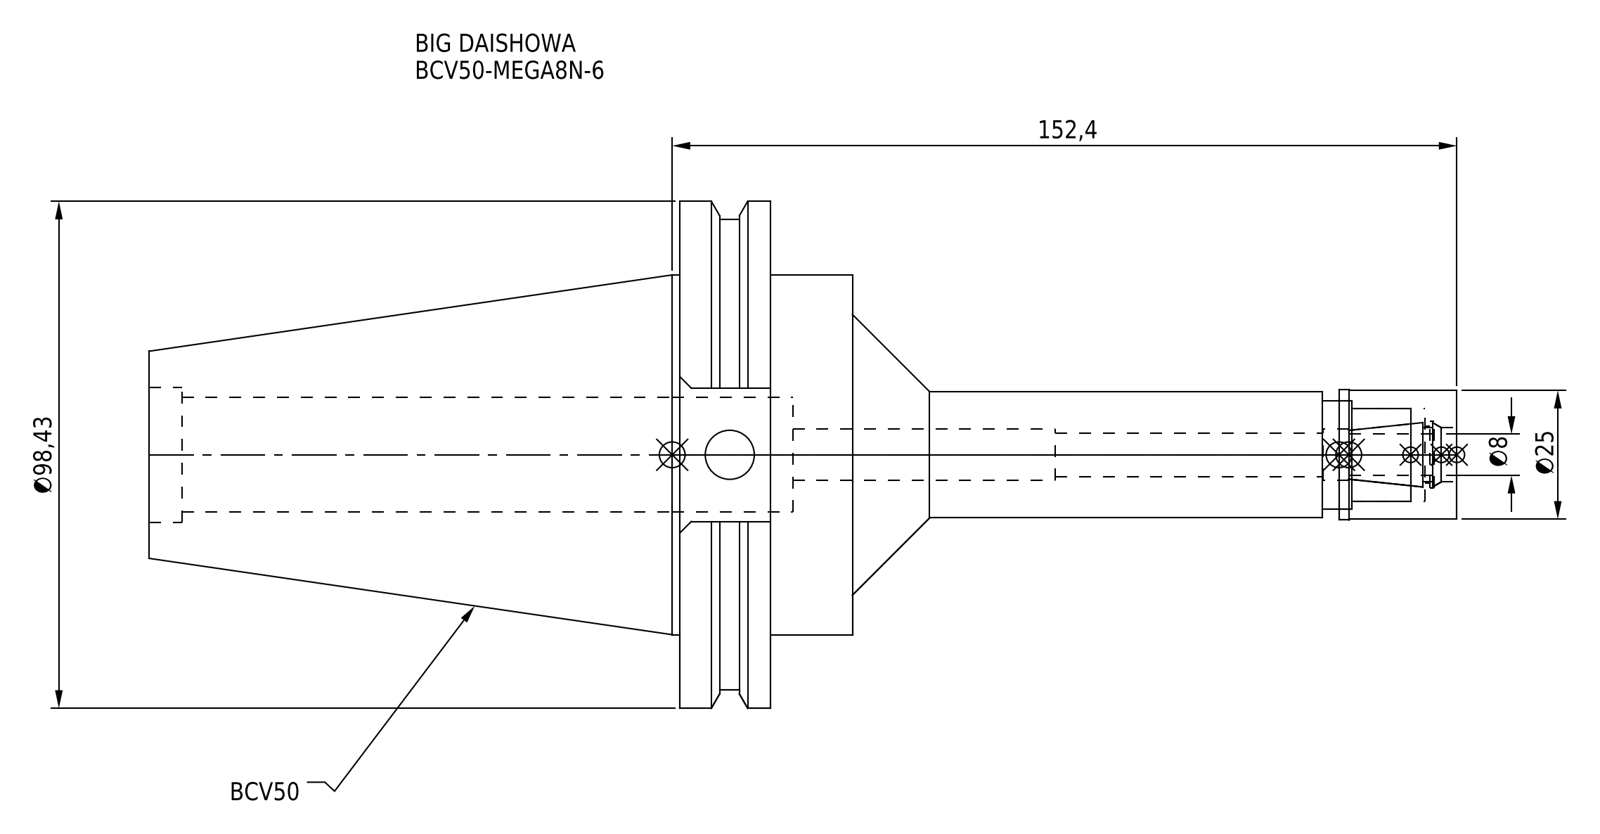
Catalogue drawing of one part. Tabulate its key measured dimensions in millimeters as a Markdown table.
| quantity | value |
| --- | --- |
| part name | BCV50-MEGA8N-6_1.stp; BCV50MN08060-080_ASM.stp; DXF_TEMP_ASSY_ASM_4_ASM.stp; MGN8_1.stp (+3 more) |
| STEP written by | SolidWorks 2019 (CONFIG_CONTROL_DESIGN) |
| units | millimeters |
| bodies | 2 solids, 91 faces (33 planar, 44 cylindrical, 14 other) |
| overall size | 254 × 98.42 × 94.95 |
| volume | 440 374 mm³ |
| surface area | 63 860 mm² |
| round holes (diameter × count) | 8.4 × 1, 9.53 × 1, 10 × 1, 10.5 × 1, 11 × 1, 13 × 1, 18 × 1, 21 × 1, 22.3 × 1, 26.23 × 1 |
| round bosses / shafts (diameter × count) | 98.42 × 1, 91.29 × 1, 69.85 × 1, 25.3 × 1, 25 × 1, 24.5 × 1 |
| main face-to-face distances | 17.55, 15.95, 33.5, 136.6, 120.65, 103.1, 117.4, 133.35, 150.9, 254 |
